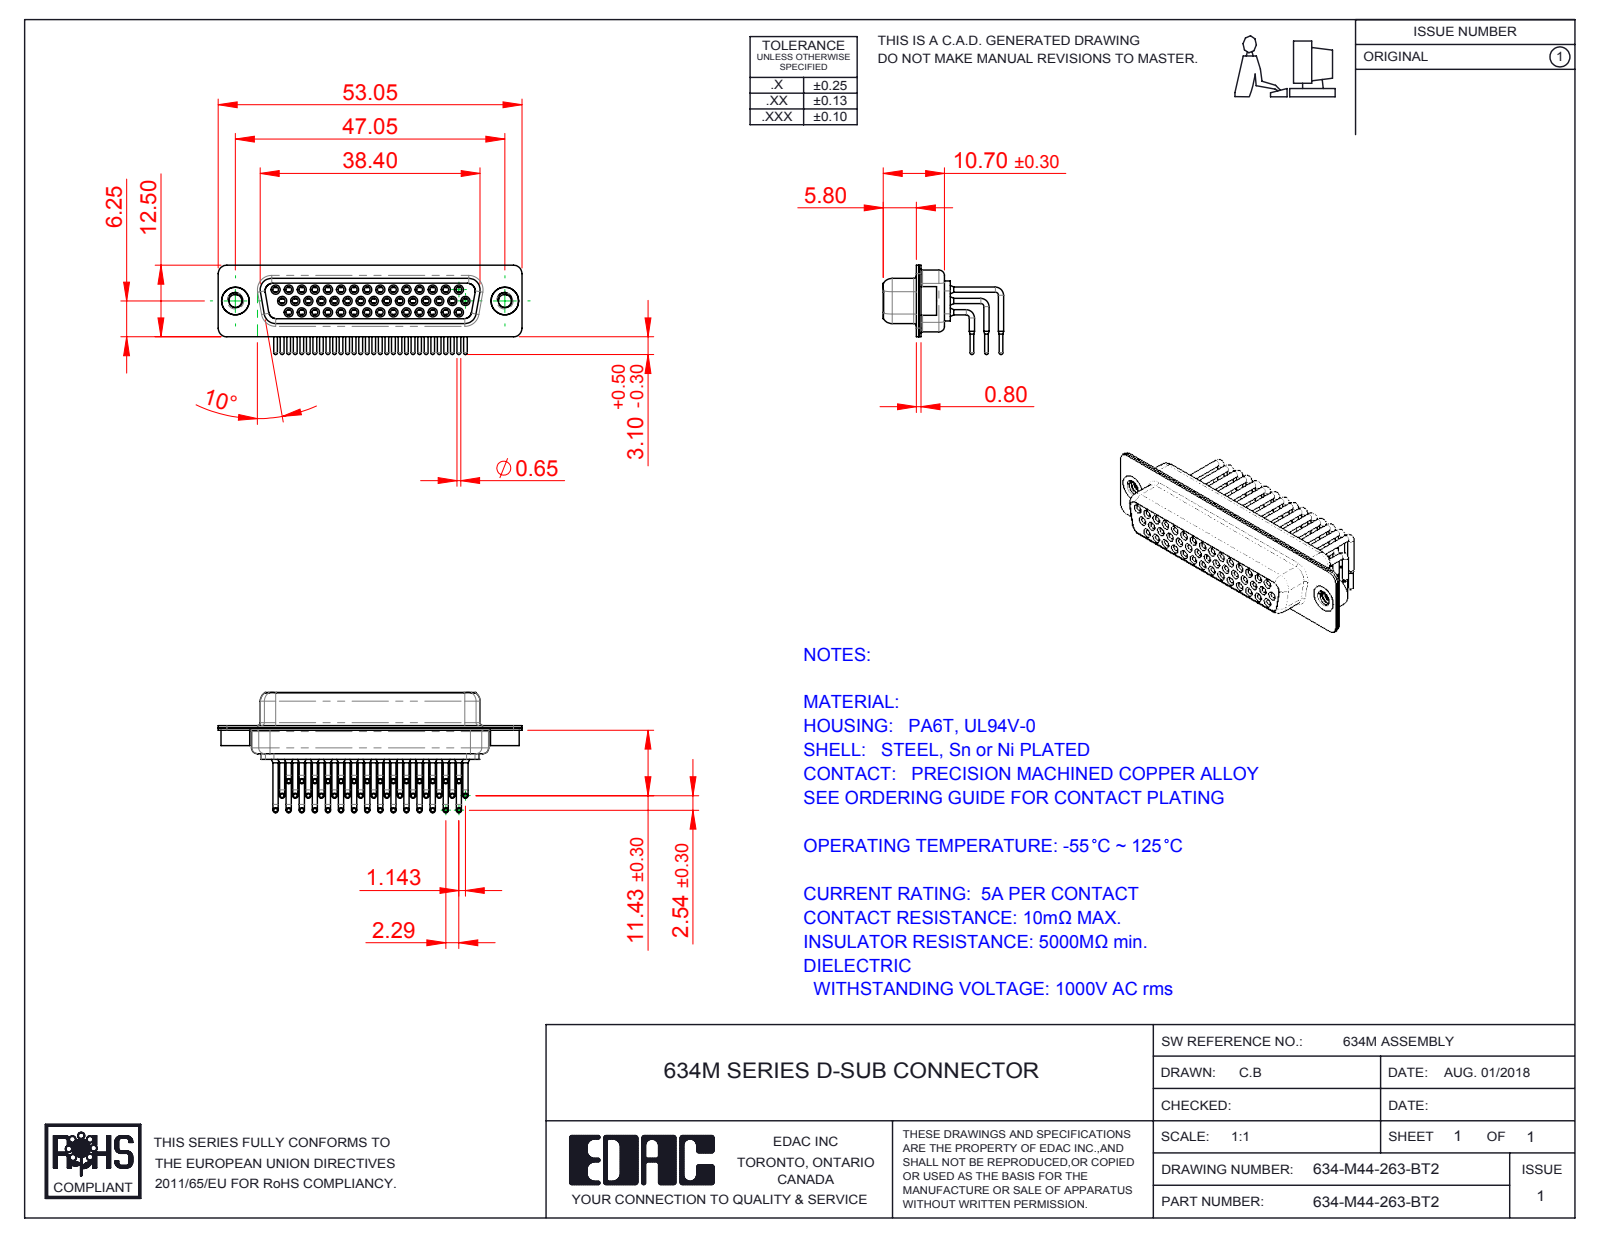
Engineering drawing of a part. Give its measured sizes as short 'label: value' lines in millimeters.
name: 634M Shell Rear_44 Contacts; 634M Shell Front_44 Contacts; 634M Contact Row 3; 634M Housing_44 Contacts (+4 more)
written by: SolidWorks 2016 (CONFIG_CONTROL_DESIGN)
unit: mm
bodies: 49 solids, 2611 faces (727 planar, 1149 cylindrical, 735 other)
size: 53.05 × 21.02 × 15.6
volume: 3 837 mm³; area: 13 038 mm²
holes: 44× ⌀1, 44× ⌀1.1, 44× ⌀1.7, 44× ⌀1.8, 44× ⌀2, 2× ⌀2.26, 2× ⌀4, 2× ⌀4.8
bosses: 88× ⌀0.9, 44× ⌀1.6, 44× ⌀1.5, 44× ⌀0.65, 2× ⌀5, 2× ⌀4.9
rounds: 16× R1.5, 12× R2, 8× R1.35, 8× R1.6, 4× R0.25, 4× R0.5, 4× R0.6, 4× R0.65
face distances: 0.4, 1.45, 8.95, 2.3, 1.9, 8.5, 6.2, 7.05, 0.45, 0.85
hole spacings: 2.28, 3.96, 2.29, 4.57, 8.24, 6.86, 11.43, 10.48
